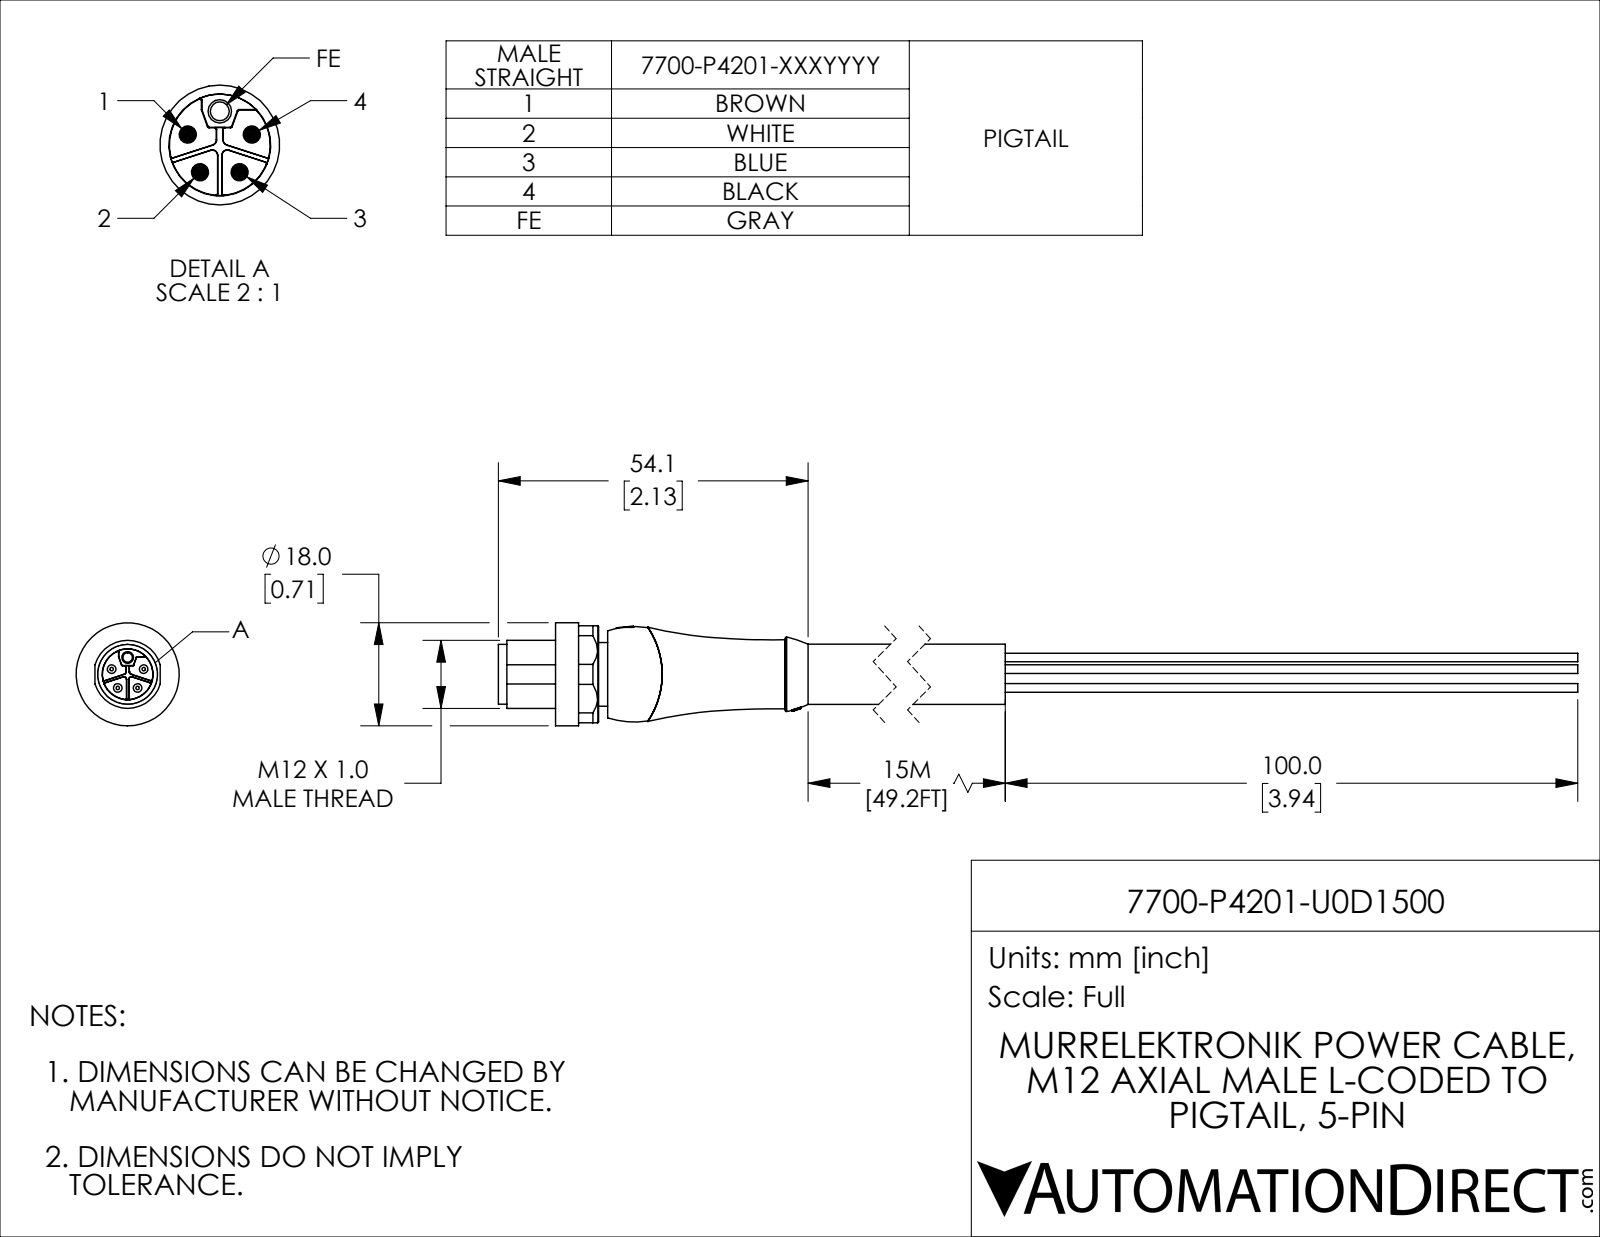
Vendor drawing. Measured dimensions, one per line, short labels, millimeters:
name: 7700-P4201-U0D1500
written by: SolidWorks 2021 (CONFIG_CONTROL_DESIGN)
unit: mm
bodies: 1 solid, 190 faces (87 planar, 51 cylindrical, 52 other)
size: 254.1 × 18 × 18
volume: 17 489 mm³; area: 9 110 mm²
holes: 1× ⌀1.65
bosses: 5× ⌀1.5, 1× ⌀18, 1× ⌀11.88, 1× ⌀11.1, 1× ⌀10.5, 1× ⌀10.45
rounds: 6× R0.15, 1× R1.13, 1× R8.95
face distances: 9.1, 1.9, 7.2, 144.1, 136.9, 135, 16.94, 1.2, 8.4, 10.3
